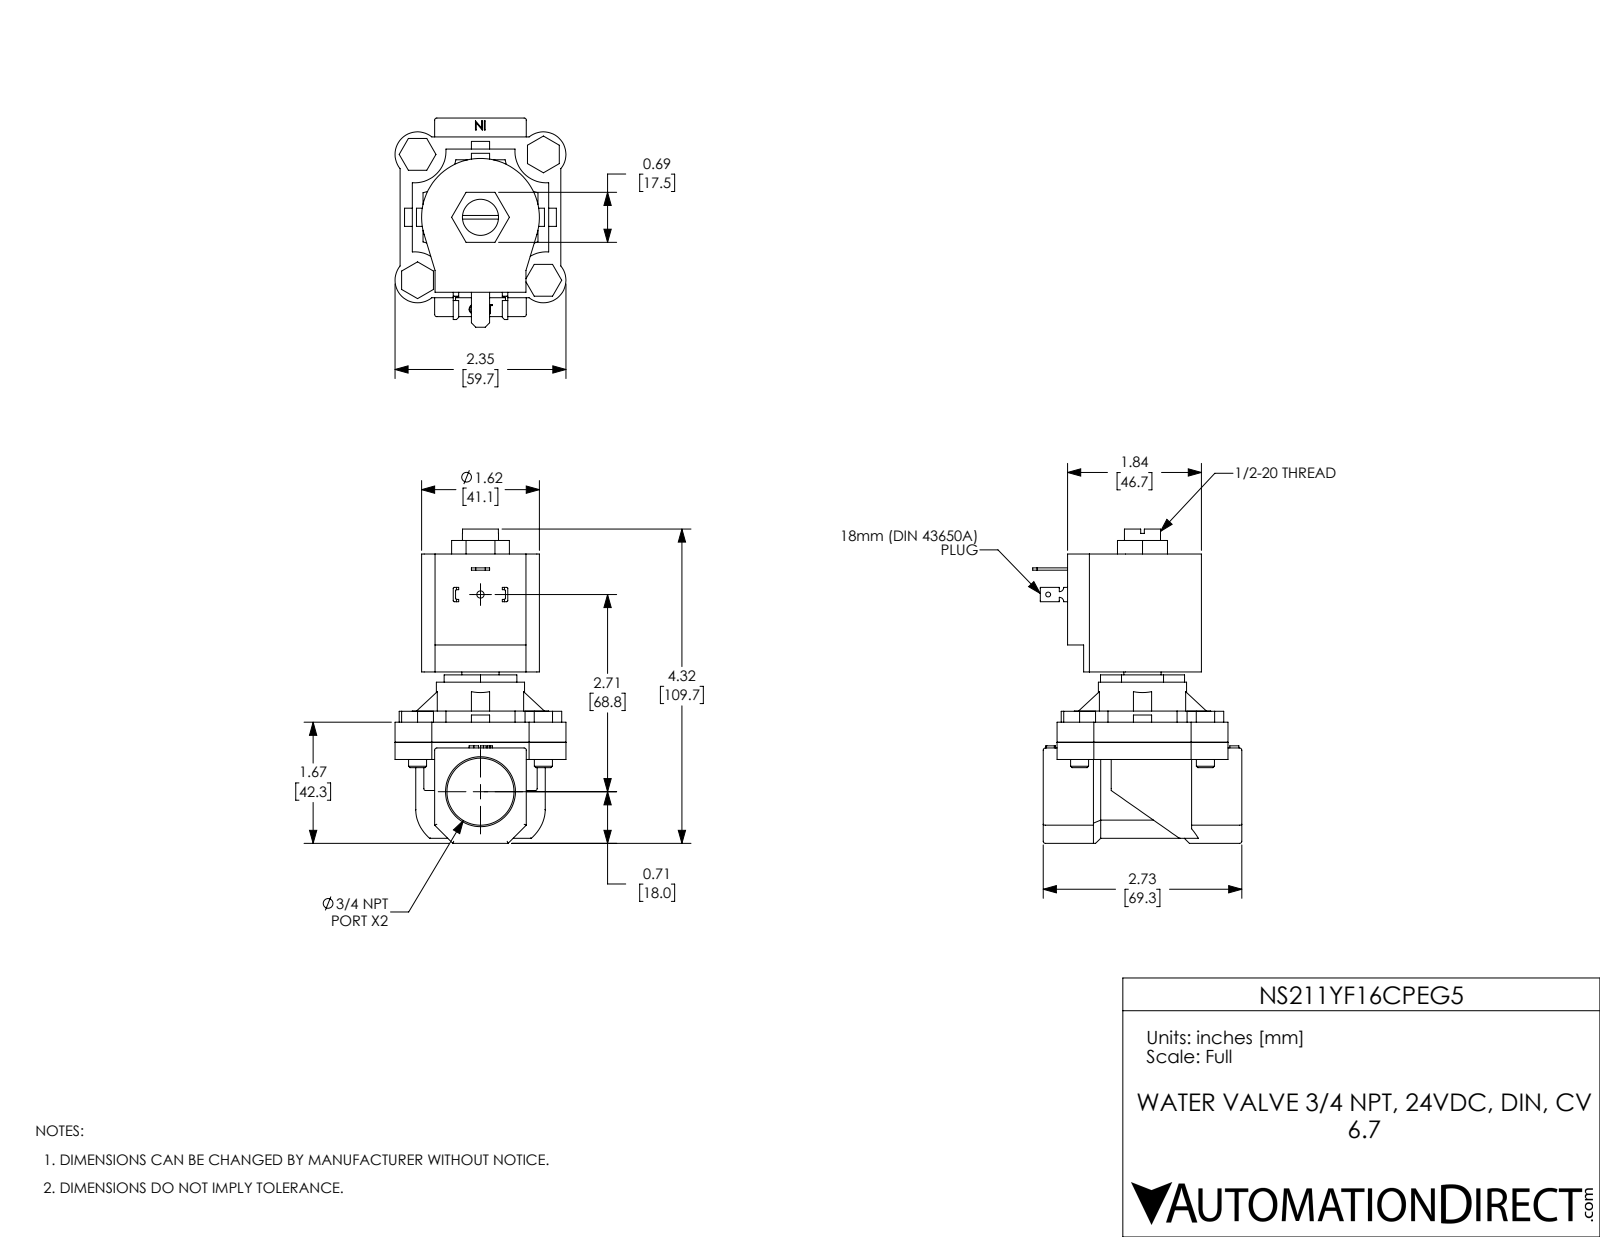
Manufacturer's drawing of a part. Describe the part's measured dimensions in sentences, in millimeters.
The part is named "NS211YF16CPEG5". Its 3-D file was written by "SolidWorks 2021 (CONFIG_CONTROL_DESIGN)". It is 11 solids with 387 faces: 241 planar, 113 cylindrical and 33 other. Overall it measures 109.7 by 73 by 59.7 millimeters. Its volume is 174 000 cubic millimeters and its surface area 45 750 square millimeters. Round holes: 4 of diameter 6.4, 1 of diameter 1.7, 1 of diameter 2.5, 1 of diameter 12.6, 1 of diameter 13, 1 of diameter 23.4, 1 of diameter 29.3. Round bosses or shafts: 4 of diameter 6.3, 1 of diameter 30.8. Partial cylindrical surfaces (rounded edges, fillets, slot ends): 15 of radius 0.8, 8 of radius 0.4, 4 of radius 7.9, 4 of radius 11, 4 of radius 14.7, 2 of radius 1.5, 1 of radius 20.6, 1 of radius 22.6. The main face-to-face distances are 7, 65.7, 58.7, 6, 13, 71.7, 12.1, 44.1, 32, 56.1. The hole center spacings are 31.1, 43.9, 62.1, 68.8.
